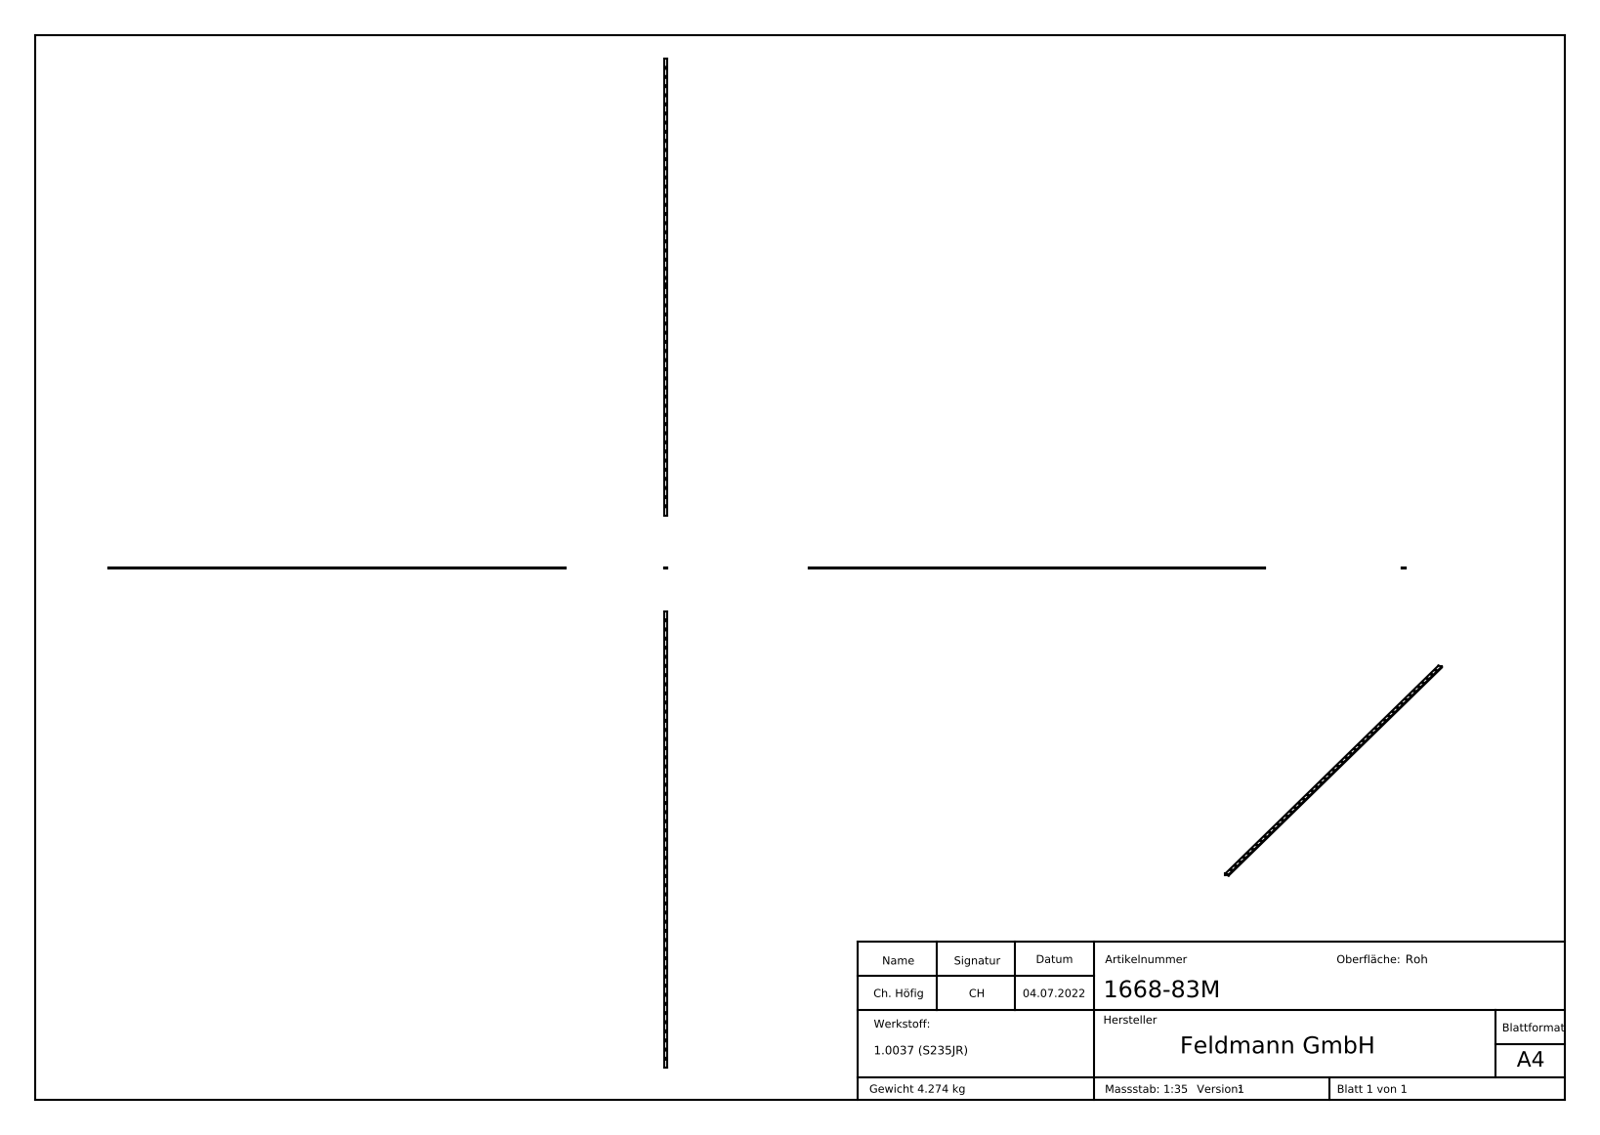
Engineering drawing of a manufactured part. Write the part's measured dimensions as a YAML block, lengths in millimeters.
part_name: "1668-83M"
step_written_by: "SolidWorks 2018 (CONFIG_CONTROL_DESIGN)"
units: millimeters
bodies: {solids: 1, faces: 323, planar: 140, cylindrical: 49, other: 134}
overall_size: [3000, 25, 8]
volume: 547968
surface_area: 201414
round_holes:
  - {diameter: 13, count: 49}
face_to_face_distances: [8, 25, 3000, 7.9, 3.27, 0.54, 3.41, 0.34, 11.49, 13.51]
hole_center_spacings: [60, 120, 180, 240, 300, 360, 420, 480]
